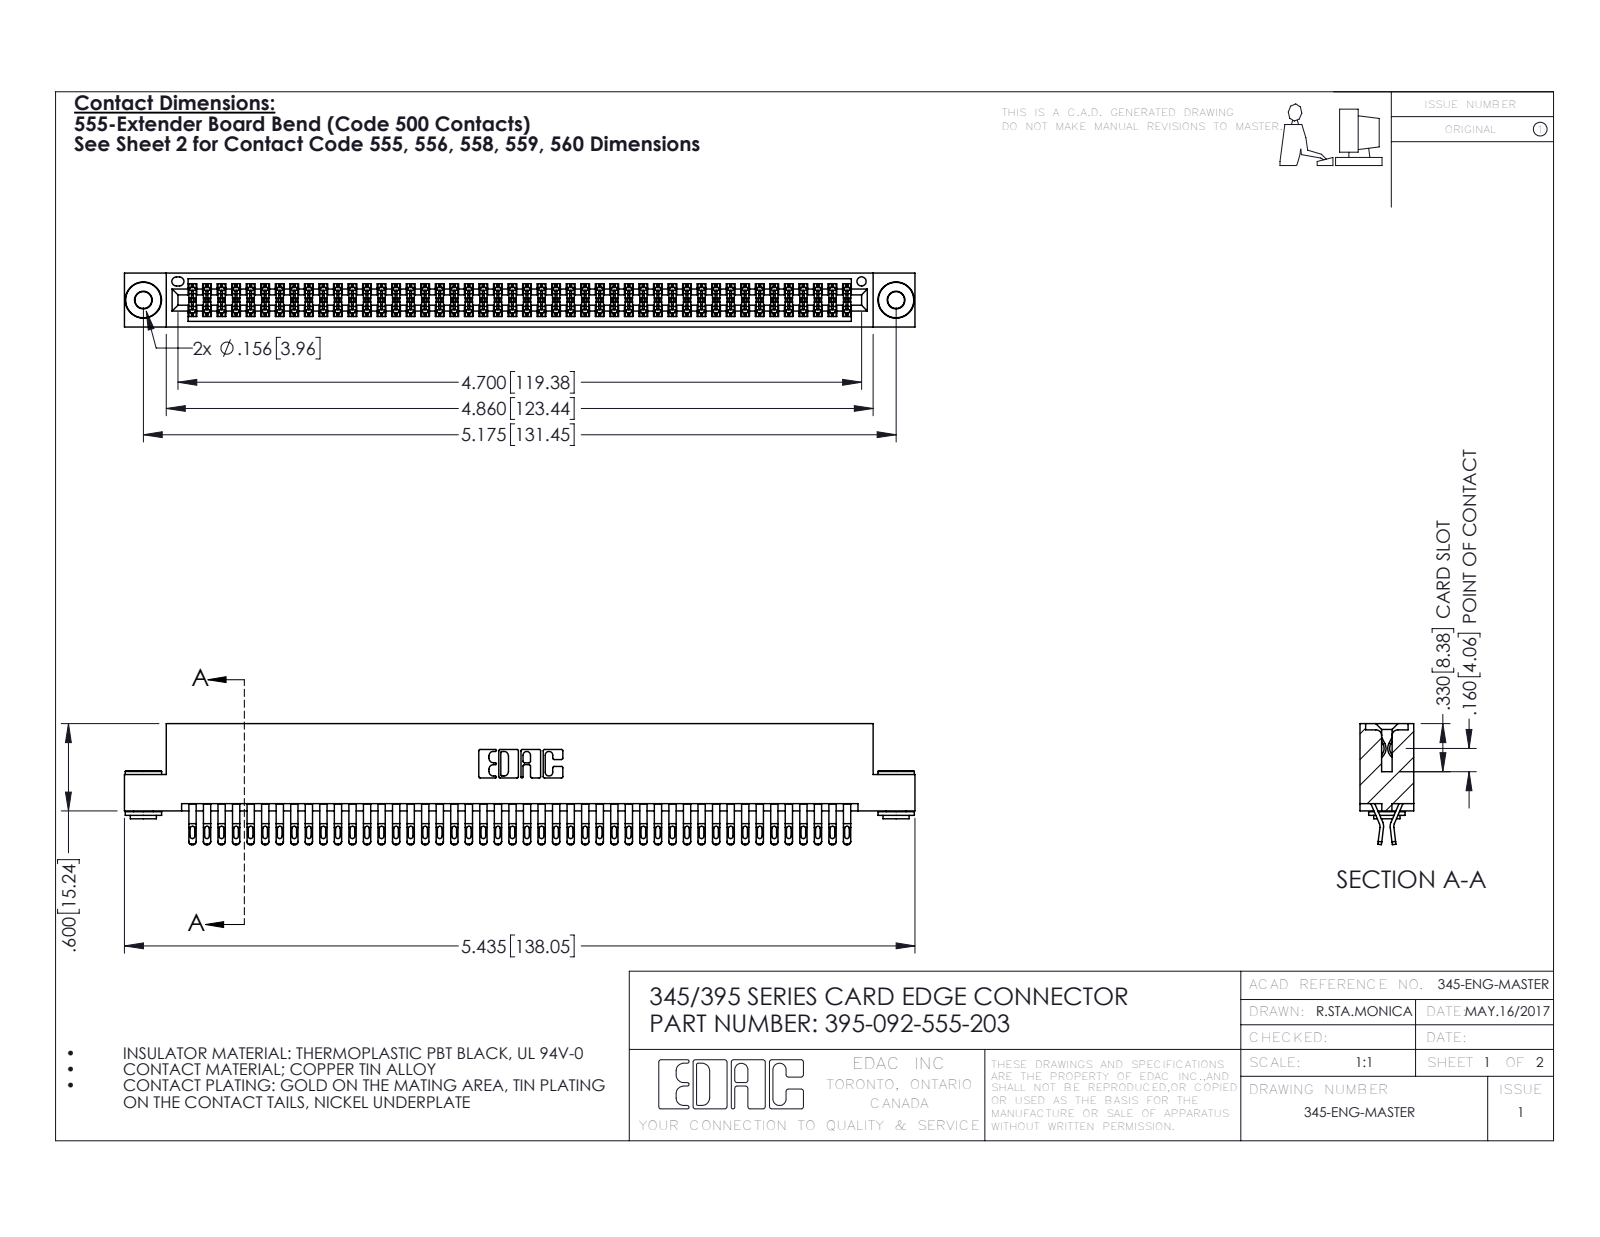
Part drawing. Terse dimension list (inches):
name: 345-292-001_555 Tail; 345 Part_Flush Mounting Lugs - 0.156 Dia-TH; 345-250-002_345-250-002-102; 395-092-555-203
written by: SolidWorks 2016 (CONFIG_CONTROL_DESIGN)
unit: in
bodies: 95 solids, 5316 faces (2942 planar, 2366 cylindrical, 8 other)
size: 5.435 × 0.832 × 0.37
volume: 0.838 in³; area: 33.34 in²
holes: 2× ⌀0.116, 2× ⌀0.156, 1× ⌀0.064
bosses: 2× ⌀0.25, 2× ⌀0.18, 2× ⌀0.136
rounds: 230× R0.016, 184× R0.02, 138× R0.006, 22× R0.01, 6× R0.007, 6× R0.031, 3× R0.026, 2× R0.01
face distances: 0.072, 0.298, 0.025, 0.2, 0.37, 0.098, 0.272, 0.225, 0.175, 0.149
hole spacings: 0.27, 4.939, 5.175
